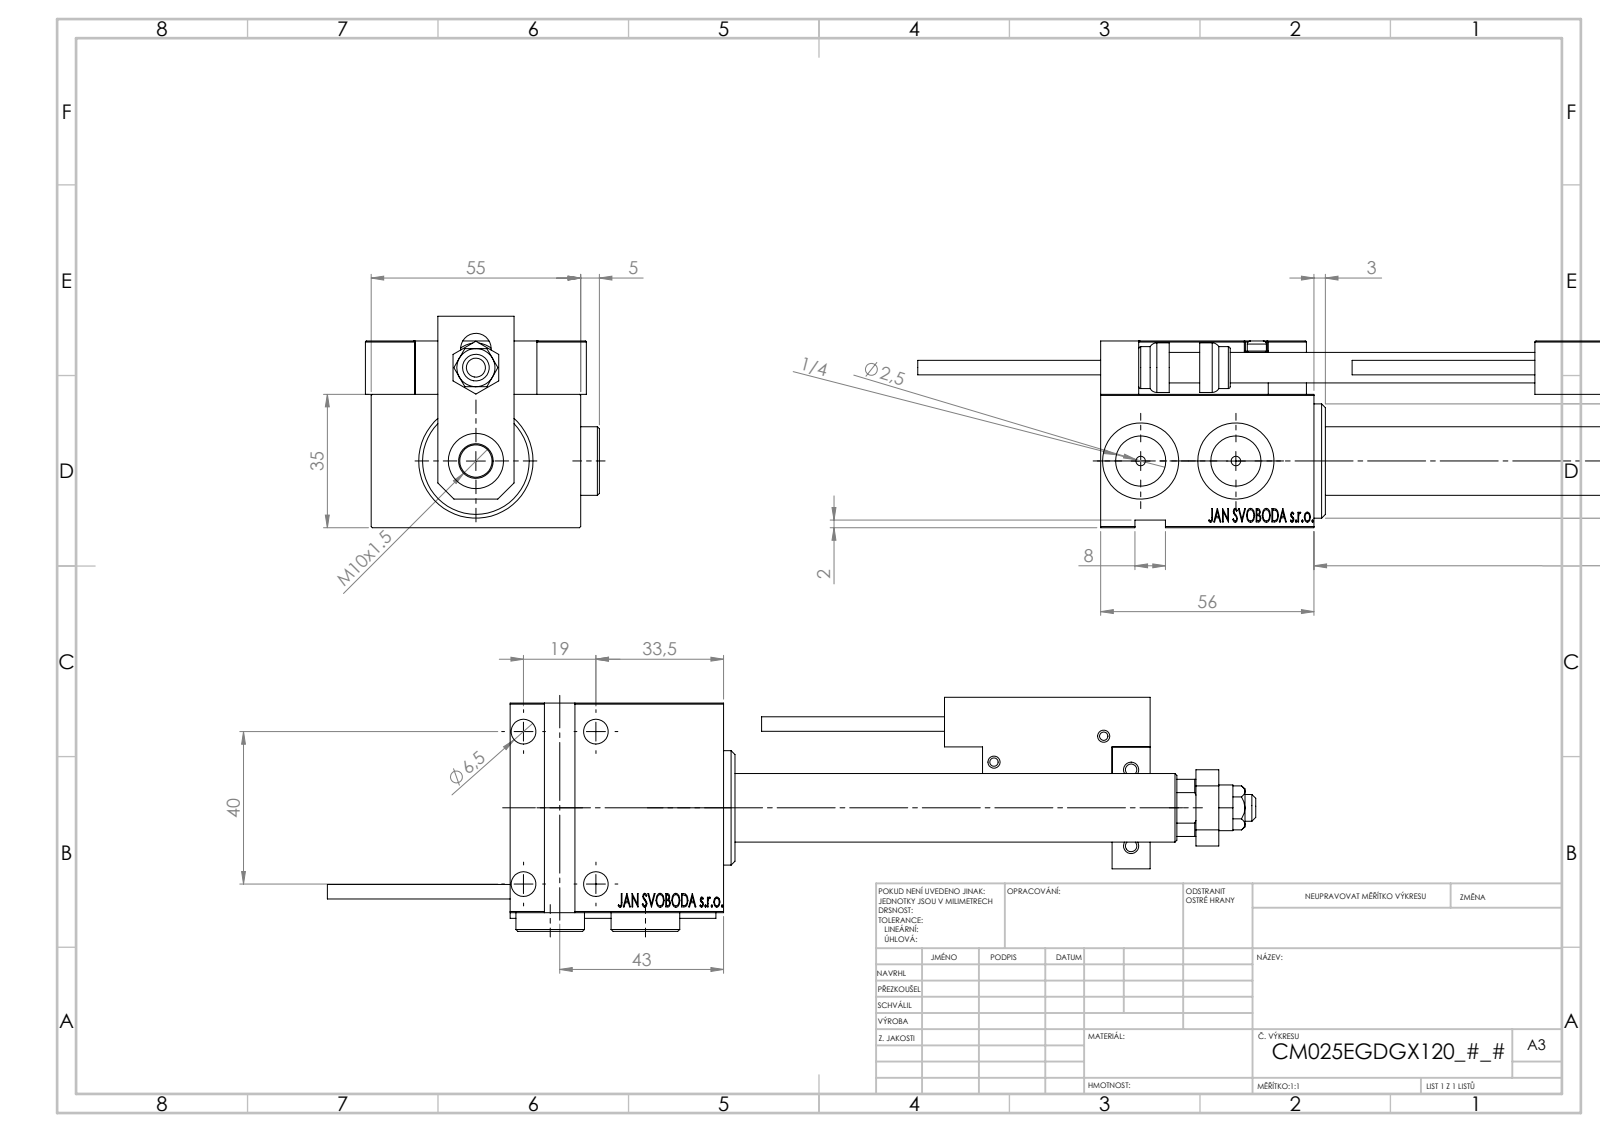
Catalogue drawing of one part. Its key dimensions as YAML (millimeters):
part_name: "Zatka_OIL_PORT; ZARAZKA; SWITCH DIM B,W; SWITCH_X_FRONT_BACK (+7 more)"
step_written_by: "SolidWorks 2019 (CONFIG_CONTROL_DESIGN)"
units: millimeters
bodies: {solids: 26, faces: 1340, planar: 601, cylindrical: 194, other: 545}
overall_size: [243.7, 61.4, 55.5]
volume: 178458
surface_area: 65950
round_holes:
  - {diameter: 8, count: 6}
  - {diameter: 3.2, count: 4}
  - {diameter: 4, count: 4}
  - {diameter: 6.5, count: 4}
  - {diameter: 2.5, count: 2}
  - {diameter: 5, count: 2}
  - {diameter: 10.5, count: 2}
  - {diameter: 13.16, count: 2}
  - {diameter: 20, count: 2}
  - {diameter: 7, count: 1}
  - {diameter: 8.5, count: 1}
  - {diameter: 14.5, count: 1}
round_bosses_or_shafts:
  - {diameter: 18, count: 2}
  - {diameter: 5, count: 2}
  - {diameter: 3.8, count: 2}
  - {diameter: 30, count: 1}
  - {diameter: 27, count: 1}
  - {diameter: 13, count: 1}
  - {diameter: 11, count: 1}
partial_cylinders:
  - {radius: 0.3, count: 30}
  - {radius: 3, count: 2}
  - {radius: 5.25, count: 2}
  - {radius: 8.5, count: 1}
face_to_face_distances: [35, 49, 14, 5, 1.5, 10, 56, 6, 56.5, 20]
hole_center_spacings: [20.16, 10.11, 11.37, 19, 20, 29.59, 29.69, 30.04]
